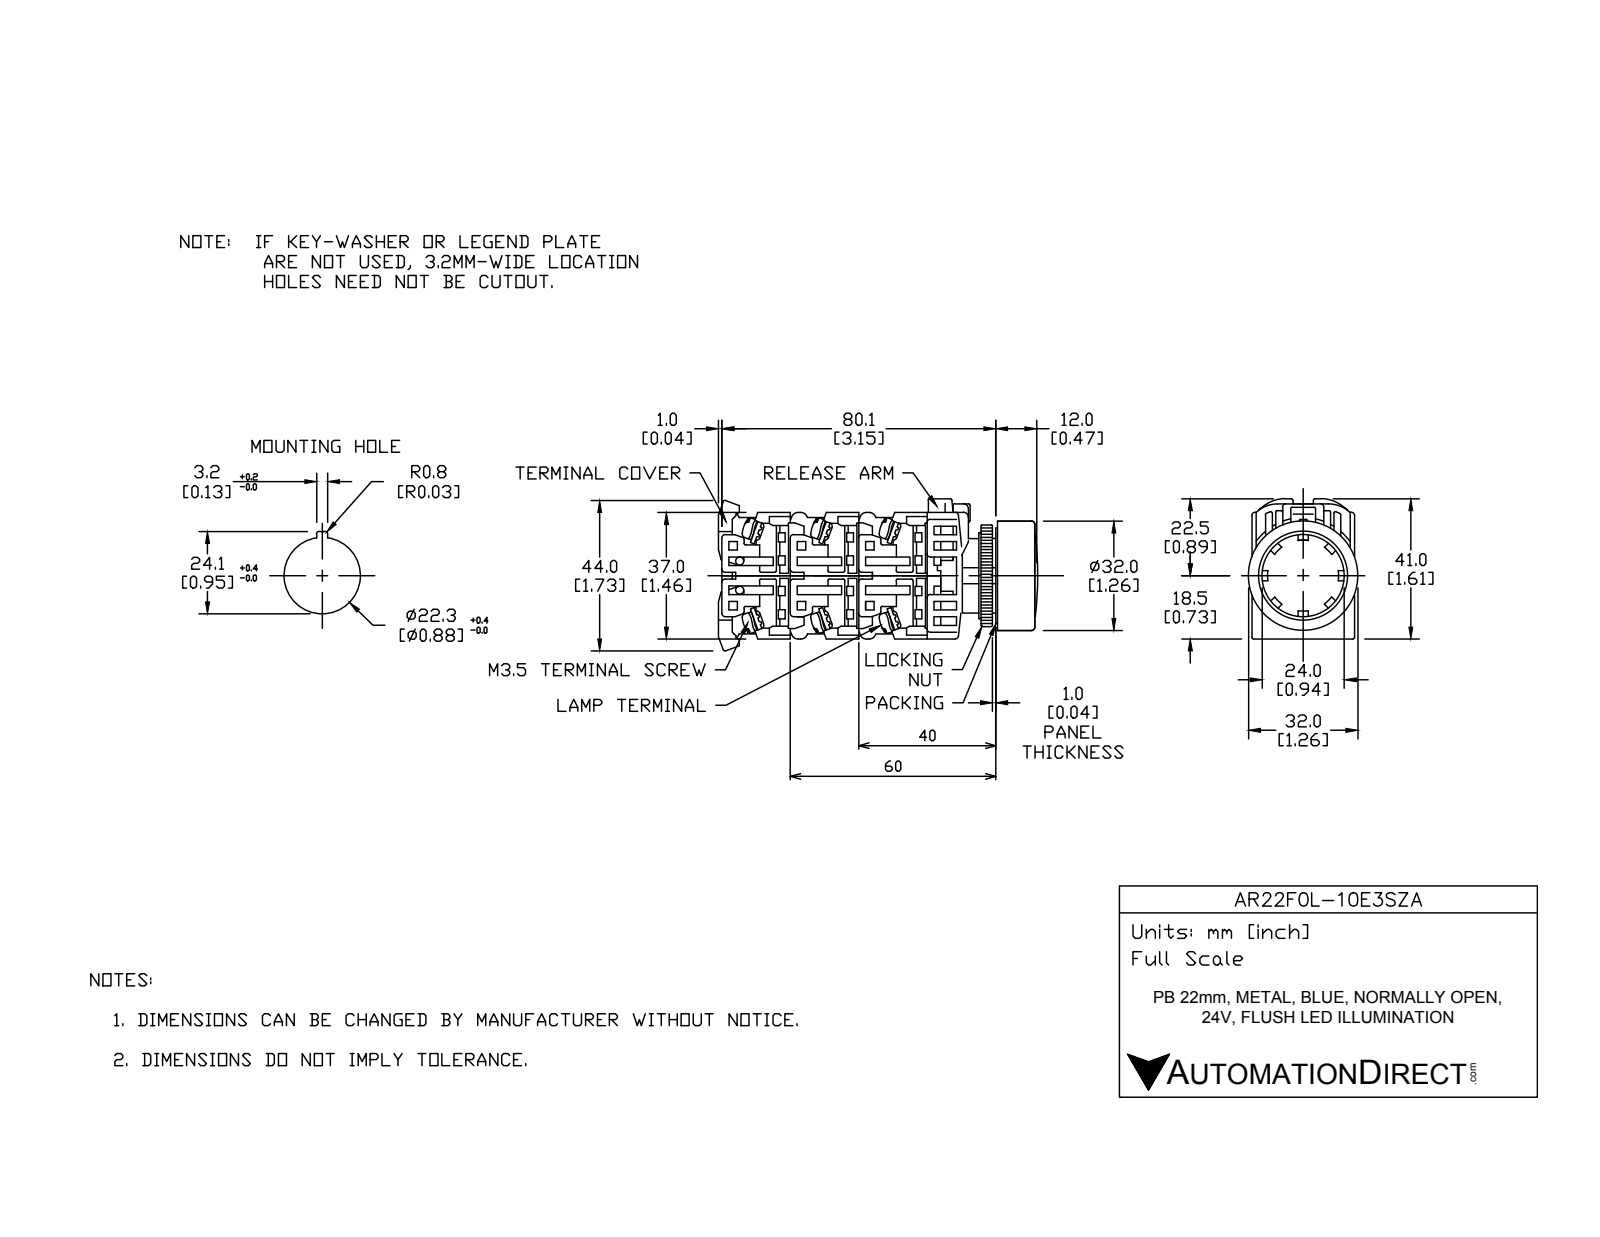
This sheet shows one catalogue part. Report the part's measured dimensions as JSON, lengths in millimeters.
{"part_name": "AR22F0L-10E3SZA", "step_written_by": "SolidWorks 2017 (AUTOMOTIVE_DESIGN)", "units": "millimeters", "bodies": {"solids": 18, "faces": 475, "planar": 329, "cylindrical": 111, "other": 35}, "overall_size": [52.75, 43.81, 32], "volume_mm3": 36367, "surface_area_mm2": 24064, "round_holes": [[21.8, 1], [22, 1], [25, 1], [31, 1]], "round_bosses_or_shafts": [[5, 4], [32, 1], [30.5, 1], [29.8, 1], [24, 1], [23.8, 1], [21.75, 1], [17, 1]], "partial_cylinders_radius": [[0.5, 39], [1.75, 8], [5, 4], [4, 2], [16.59, 1], [17.59, 1]], "face_to_face_distances": [1, 18, 28.5, 48.5, 20, 29, 3, 2, 21, 0.5]}
